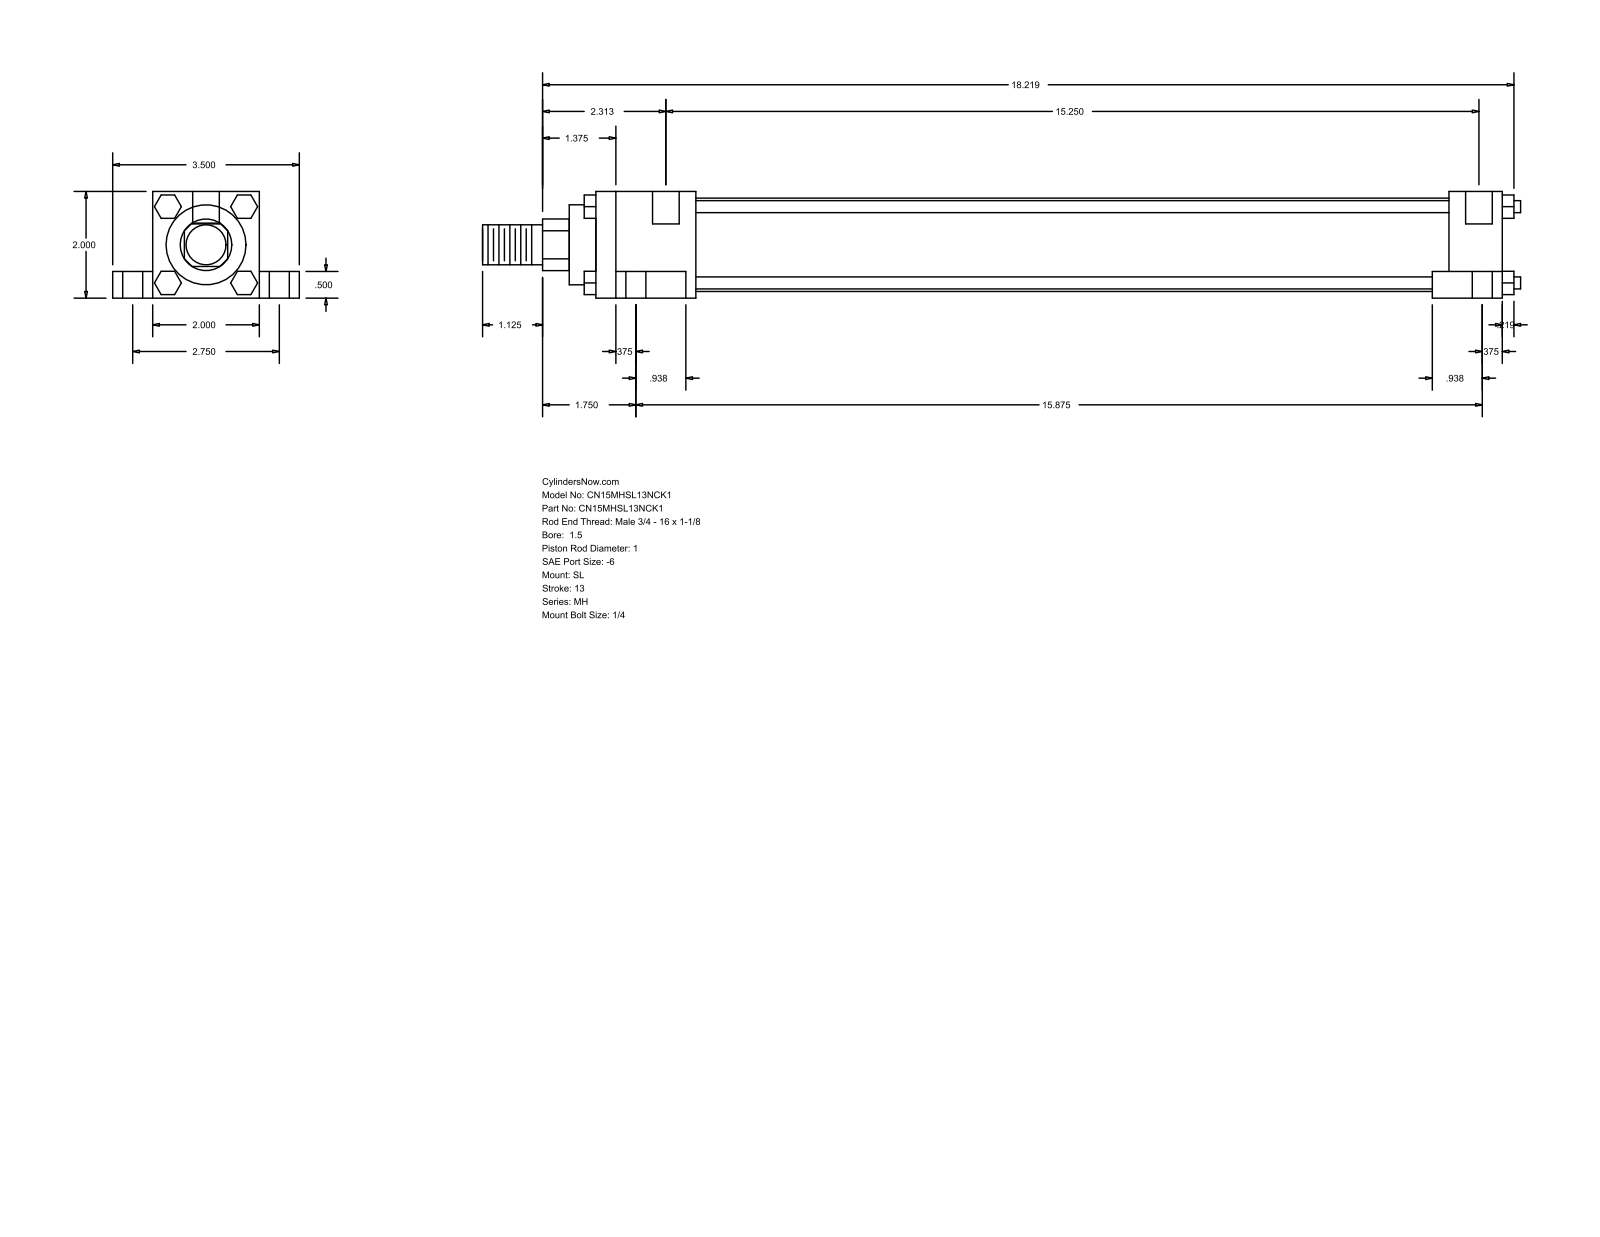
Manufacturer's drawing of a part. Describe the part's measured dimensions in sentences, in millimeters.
The part is named "MH_SL__0150_1". Its 3-D file was written by "GSSL Pune (CONFIG_CONTROL_DESIGN)". It is 0 solids with 148 faces: 112 planar, 36 cylindrical and 0 other. Overall it measures 494.51 by 88.9 by 50.8 millimeters. Round holes: 4 of diameter 5.56, 4 of diameter 9.53, 4 of diameter 15.88, 2 of diameter 12.7. Round bosses or shafts: 4 of diameter 5.71, 1 of diameter 44.45, 1 of diameter 38.1, 1 of diameter 25.4, 1 of diameter 19.05. Partial cylindrical surfaces (rounded edges, fillets, slot ends): 1 of radius 12.29. The main face-to-face distances are 50.8, 12.7, 38.1, 19.05, 69.85, 431.8, 25.4, 9.52, 33.34, 388.94. The hole center spacings are 34.96, 36.64, 37.73, 69.84, 390.5, 390.53, 393.67, 403.16.
